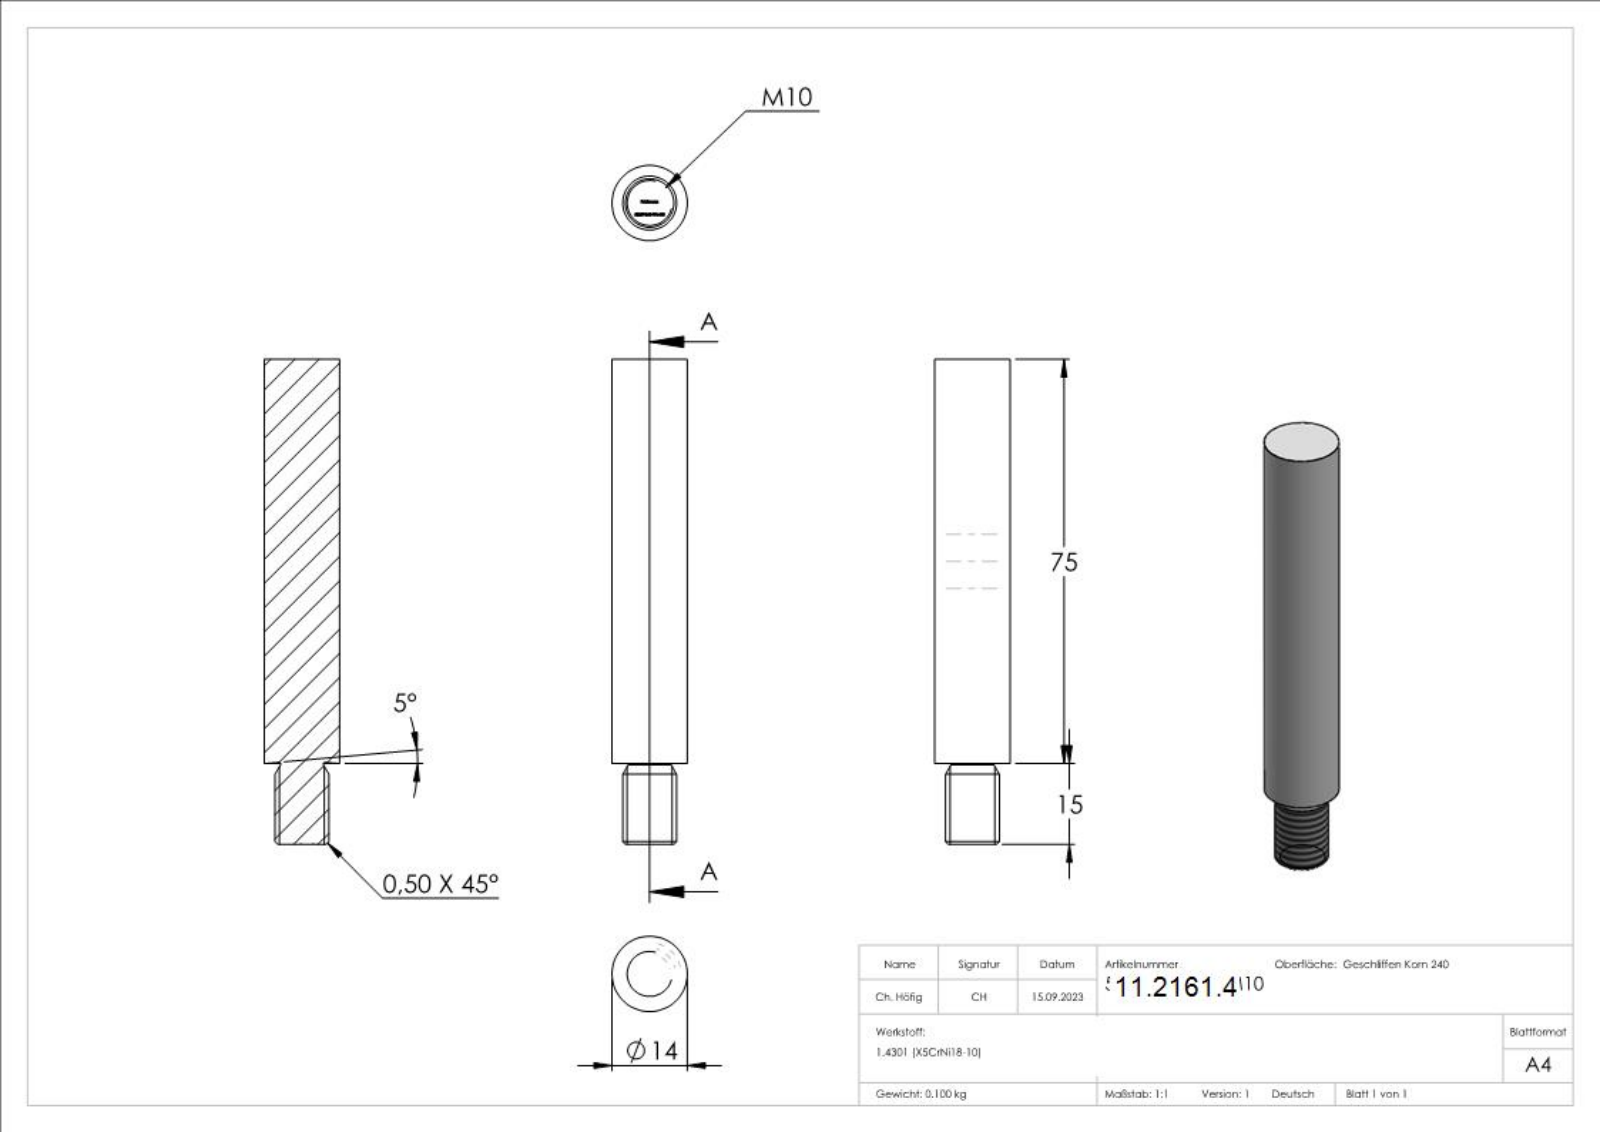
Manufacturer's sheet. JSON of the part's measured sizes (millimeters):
{"part_name": "50237-240-75-M10", "step_written_by": "SolidWorks 2018 (CONFIG_CONTROL_DESIGN)", "units": "millimeters", "bodies": {"solids": 1, "faces": 293, "planar": 170, "cylindrical": 2, "other": 121}, "overall_size": [90, 14, 14], "volume_mm3": 12674, "surface_area_mm2": 4106, "round_bosses_or_shafts": [[14, 1], [10, 1]], "face_to_face_distances": [90, 89.9, 0.47, 2.38, 0.53, 1.39, 2.39, 0.72, 2.44, 1.44]}
